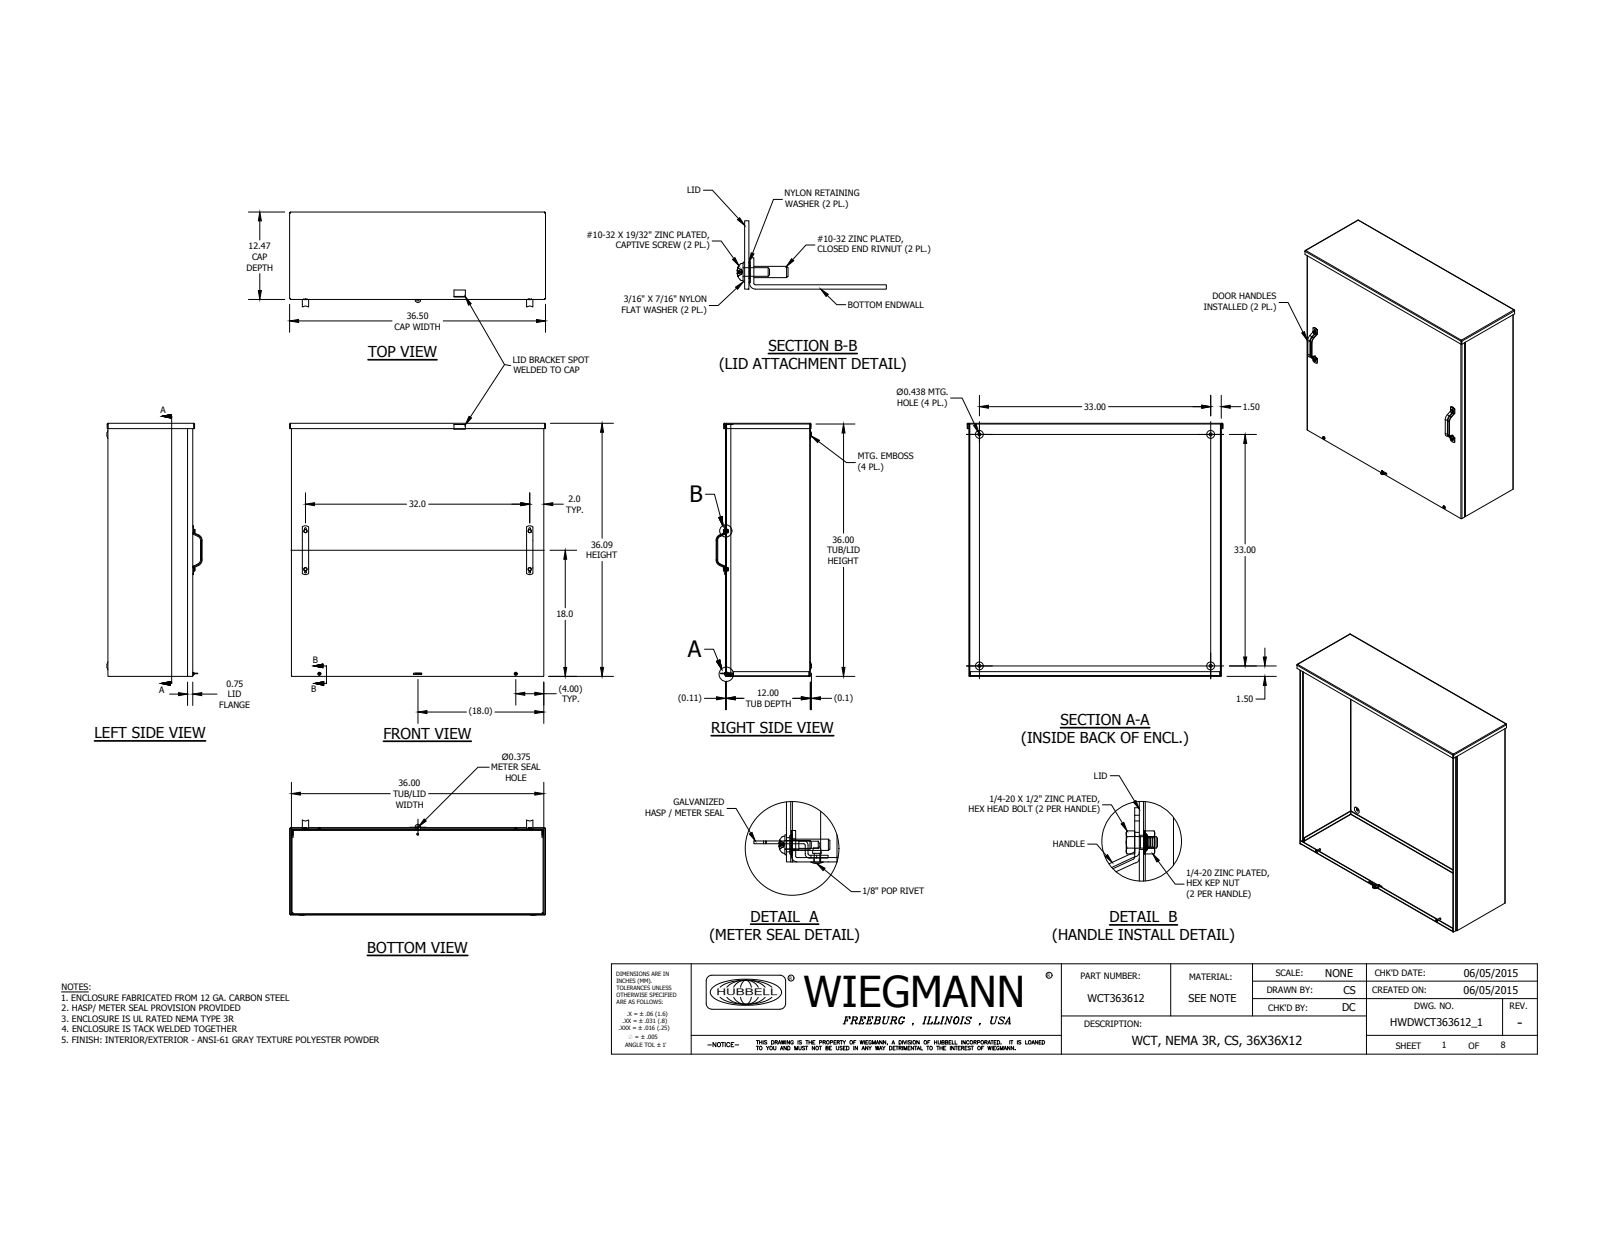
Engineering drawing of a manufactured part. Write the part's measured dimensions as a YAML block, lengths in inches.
part_name: "WCT363612BKP; WCT3612BTM; WCT3636LID; WCT3612CAP (+8 more)"
step_written_by: "Autodesk Inventor 2014 (AUTOMOTIVE_DESIGN)"
units: inches
bodies: {solids: 30, faces: 1094, planar: 540, cylindrical: 315, other: 239}
overall_size: [36.5, 36.134, 13.587]
volume: 422.7
surface_area: 9088
round_holes:
  - {diameter: 0.313, count: 6}
  - {diameter: 0.19, count: 4}
  - {diameter: 0.25, count: 4}
  - {diameter: 0.289, count: 4}
  - {diameter: 0.335, count: 4}
  - {diameter: 0.38, count: 4}
  - {diameter: 0.437, count: 4}
  - {diameter: 0.125, count: 2}
  - {diameter: 0.156, count: 2}
  - {diameter: 0.188, count: 2}
  - {diameter: 0.196, count: 2}
  - {diameter: 0.257, count: 2}
round_bosses_or_shafts:
  - {diameter: 0.438, count: 4}
  - {diameter: 0.375, count: 4}
  - {diameter: 0.33, count: 4}
  - {diameter: 0.28, count: 4}
  - {diameter: 0.453, count: 2}
  - {diameter: 0.437, count: 2}
  - {diameter: 0.406, count: 2}
  - {diameter: 0.373, count: 2}
partial_cylinders:
  - {radius: 0.02, count: 96}
  - {radius: 0.031, count: 19}
  - {radius: 0.125, count: 16}
  - {radius: 0.05, count: 8}
  - {radius: 0.1, count: 8}
  - {radius: 0.2, count: 8}
  - {radius: 0.194, count: 4}
  - {radius: 0.696, count: 4}
face_to_face_distances: [0.094, 12.016, 12.109, 11.922, 36, 35.906, 35.813, 36.094, 0.149, 35.757]
hole_center_spacings: [13.79, 19.226, 33, 35.301, 37.757, 30.521, 32, 33.167]
